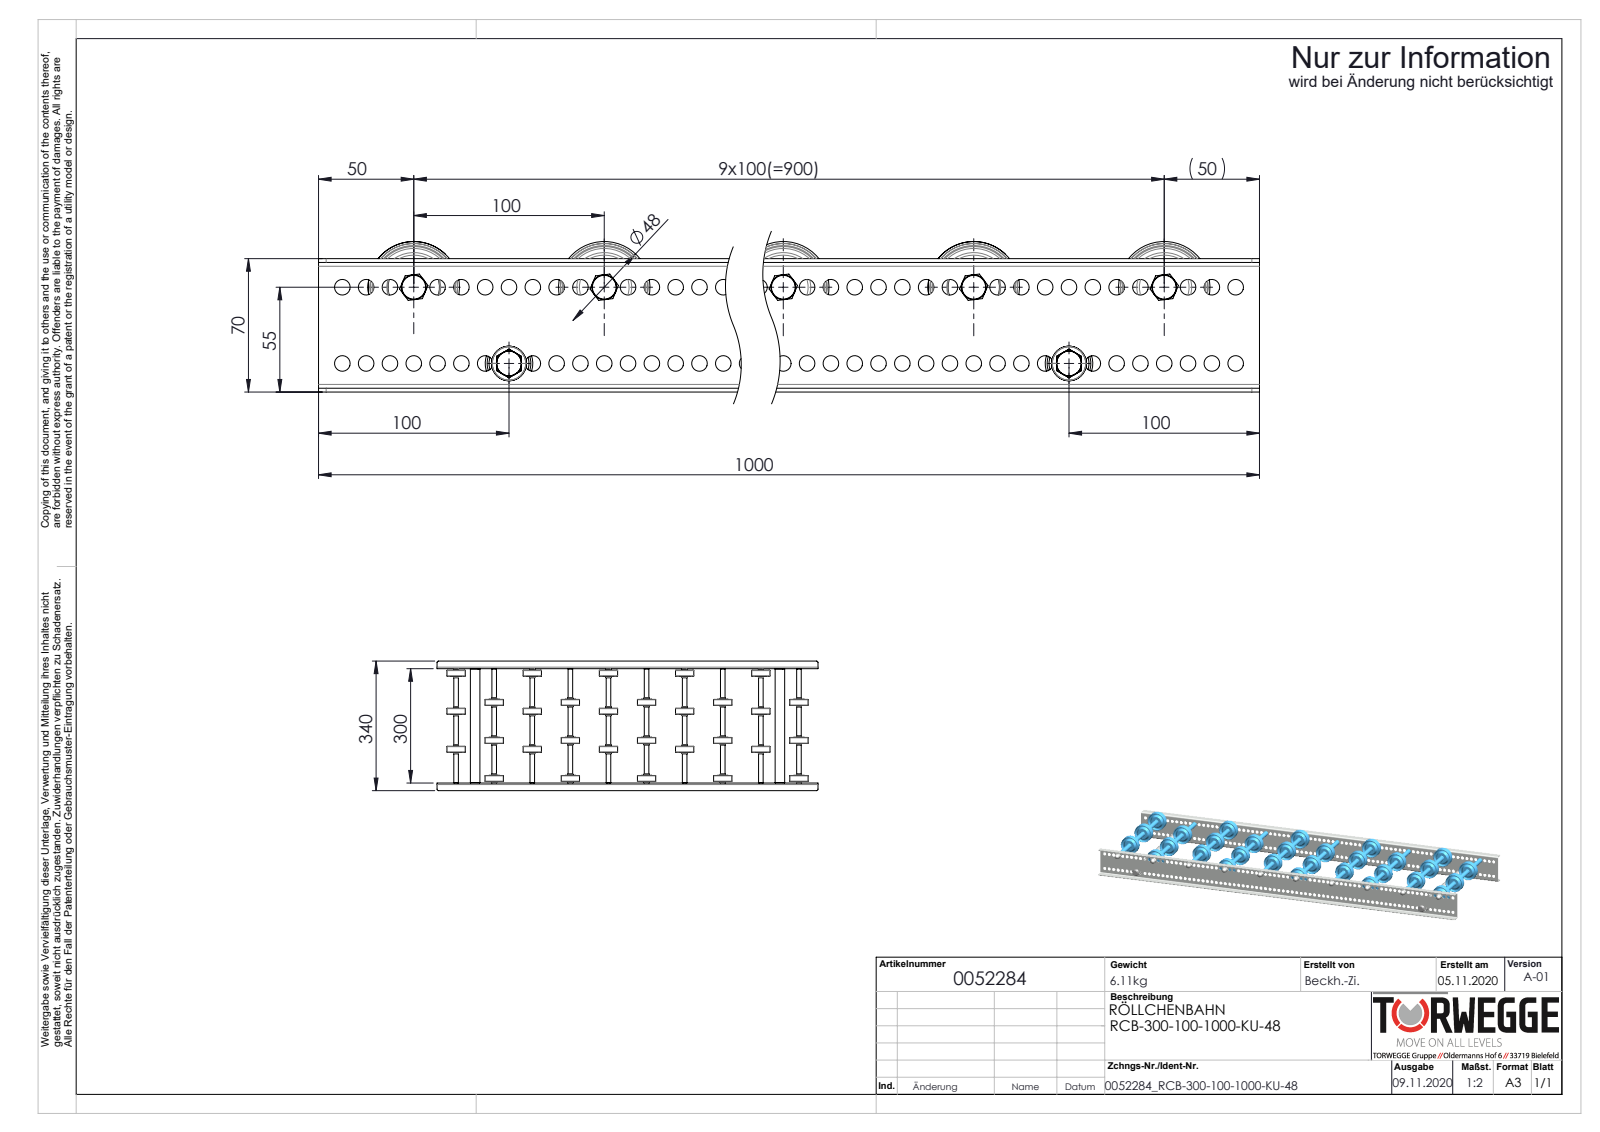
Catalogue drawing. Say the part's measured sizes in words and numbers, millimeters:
The part is named "Röllchenachse-für-Konfiguration_EL300; 0052284; 0011532_2300-48-8; S106837_Gewindestange-M8-KFG_L320 (+5 more)". Its 3-D file was written by "SolidWorks 2020 (AUTOMOTIVE_DESIGN)". It is 102 solids with 3802 faces: 690 planar, 1448 cylindrical and 1664 other. Overall it measures 1000 by 340 by 79 millimeters. Its volume is 1 339 000 cubic millimeters and its surface area 1 049 000 square millimeters. Round holes: 158 of diameter 8.2, 10 of diameter 6.65, 10 of diameter 9.65, 10 of diameter 13.7, 2 of diameter 6.8, 2 of diameter 21. Round bosses or shafts: 12 of diameter 8, 10 of diameter 48, 10 of diameter 27, 10 of diameter 12.7, 10 of diameter 12.5, 10 of diameter 12, 2 of diameter 25. Partial cylindrical surfaces (rounded edges, fillets, slot ends): 8 of radius 4, 4 of radius 2. The main face-to-face distances are 2, 302, 68, 304, 300, 66, 70, 99.8, 16.3, 76.1. The hole center spacings are 12.5, 25, 37.5, 50, 62.5, 75, 87.5, 100.
